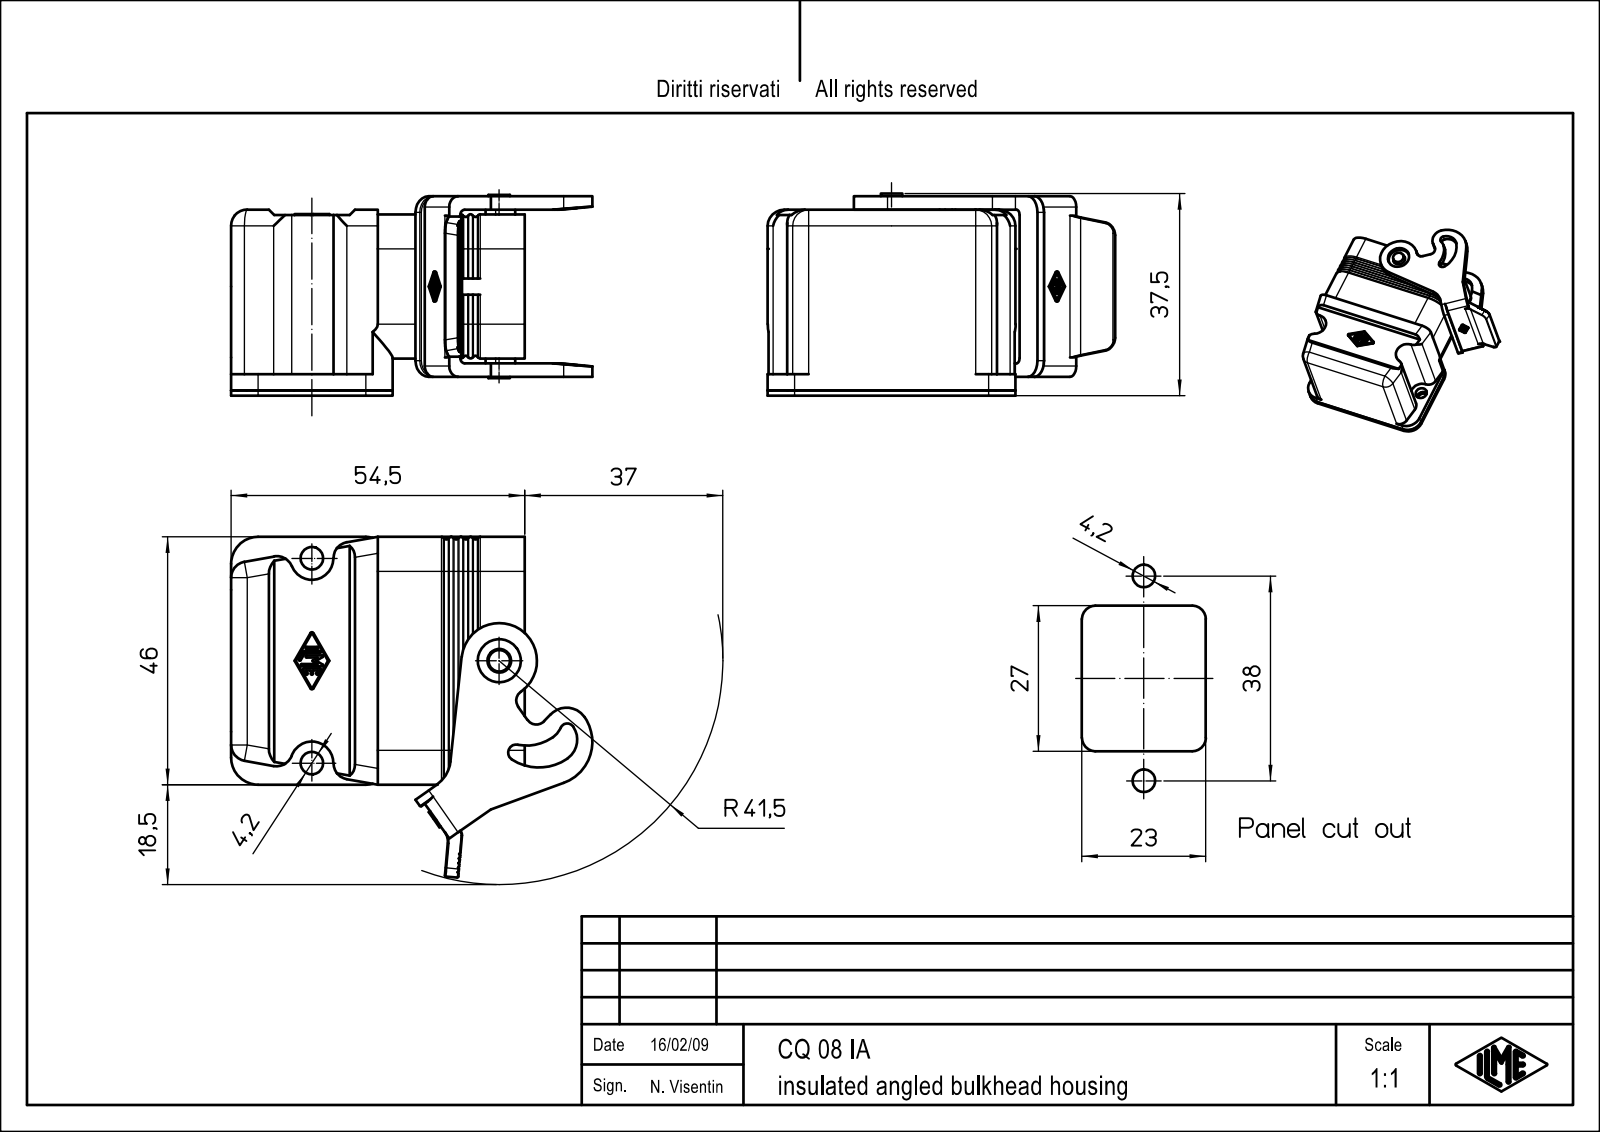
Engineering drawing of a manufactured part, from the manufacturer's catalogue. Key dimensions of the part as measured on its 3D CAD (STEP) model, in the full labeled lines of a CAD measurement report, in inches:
Part name (STEP PRODUCT): CUSTODIA_CQ_08_IA; LEVA_CQ_08_IAP; CQ_08_IA
STEP written by: CoCreate Modeling 16.00A 16-Aug-2008 (C) Parametric Technology GmbH (AUTOMOTIVE_DESIGN)
Units: inches
Bodies: 2 solids, 699 faces (269 planar, 280 cylindrical, 150 other)
Overall size (bounding box): 2.64 × 2.488 × 1.467
Volume: 1.707 in³ · Surface area: 36.92 in²
Round holes (diameter × count): ⌀0.094 ×4, ⌀0.098 ×4, ⌀0.122 ×4, ⌀0.165 ×2, ⌀0.173 ×1, ⌀0.315 ×1
Round bosses / shafts (diameter × count): ⌀0.157 ×1
Partial cylindrical surfaces — rounded edges, fillets, slot ends (radius × count): R0.02 ×36, R0.004 ×14, R0.008 ×13, R0.118 ×13, R0.079 ×9, R0.098 ×5, R0.067 ×4, R0.177 ×4
Main face-to-face distances: 0.098, 1.083, 1.319, 0.108, 1.014, 0.138, 0.207, 1.112, 0.039, 1.22
Hole centre spacings: 0.287, 0.528, 1.268, 1.373, 1.407, 1.273, 1.559, 1.751
